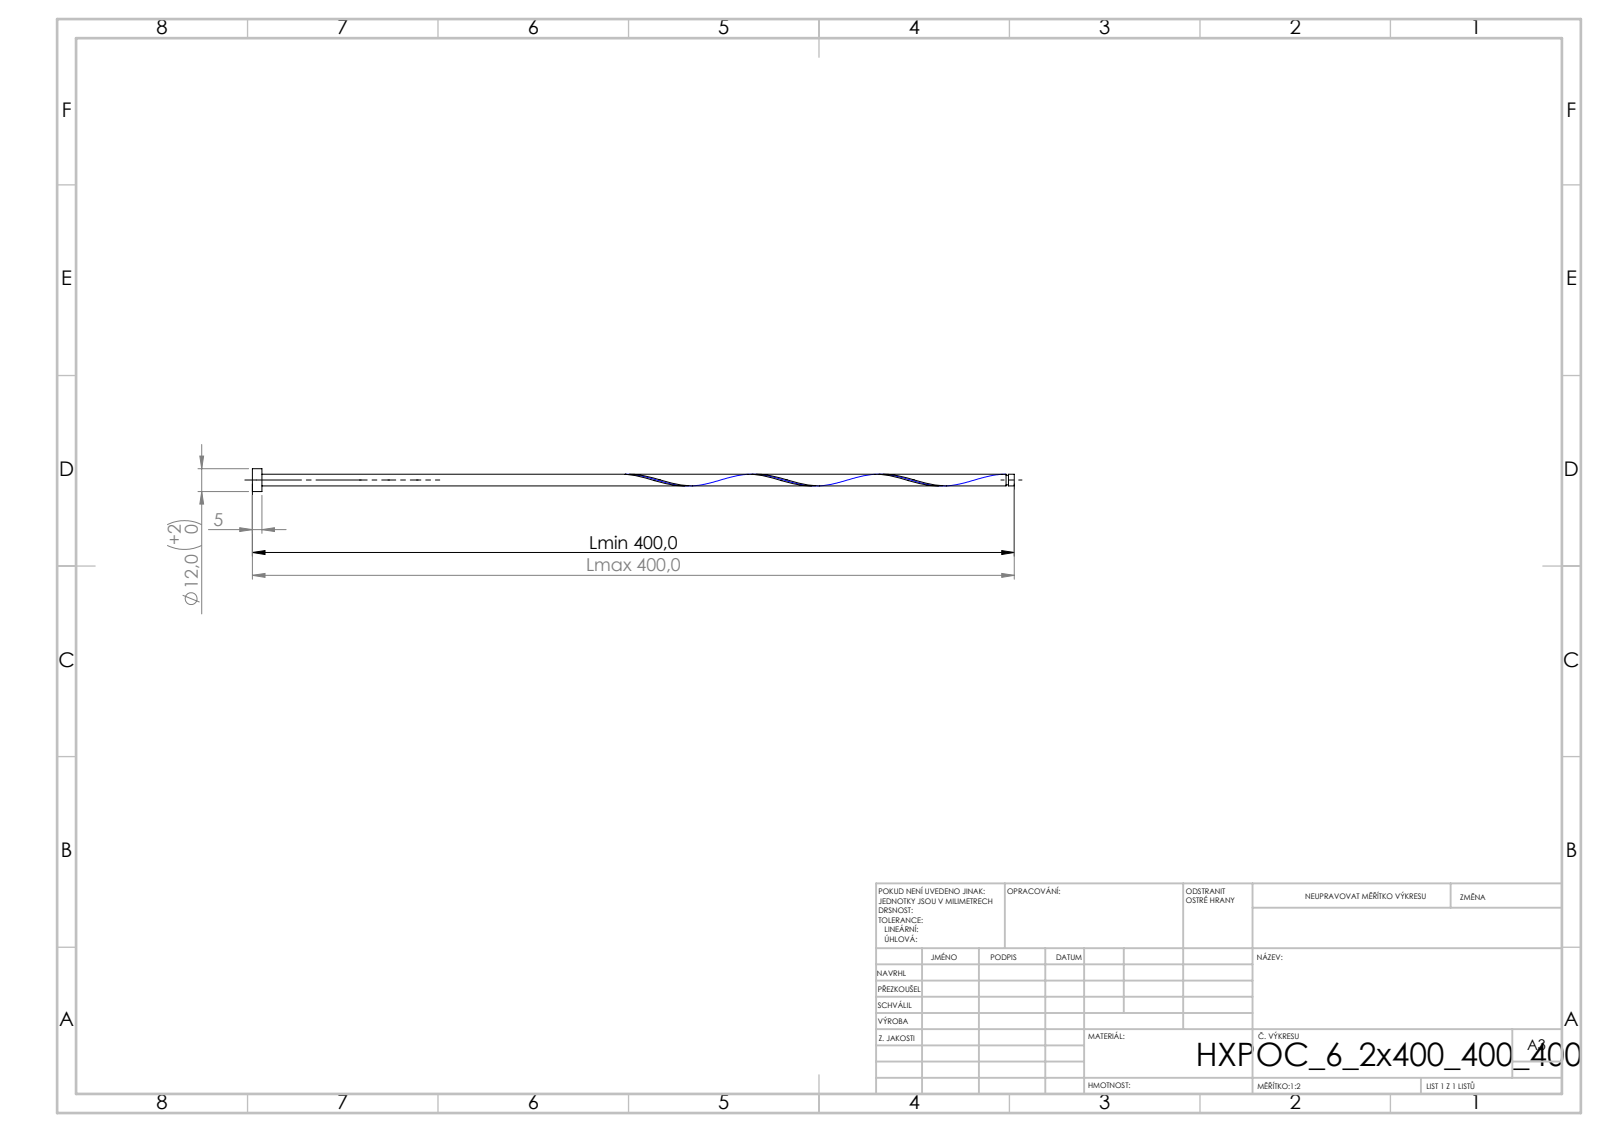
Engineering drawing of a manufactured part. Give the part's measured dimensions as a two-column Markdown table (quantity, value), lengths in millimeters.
| quantity | value |
| --- | --- |
| STEP written by | SolidWorks 2019 (CONFIG_CONTROL_DESIGN) |
| units | millimeters |
| bodies | 1 solid, 16 faces (6 planar, 9 cylindrical, 1 other) |
| overall size | 400 × 12 × 12 |
| volume | 15 047 mm³ |
| surface area | 10 847 mm² |
| round bosses / shafts (diameter × count) | 12 × 1, 6.2 × 1, 4.96 × 1 |
| main face-to-face distances | 5, 400, 395, 396.93, 391.93, 3.07, 395.69, 390.69, 1.24, 4.31 |
